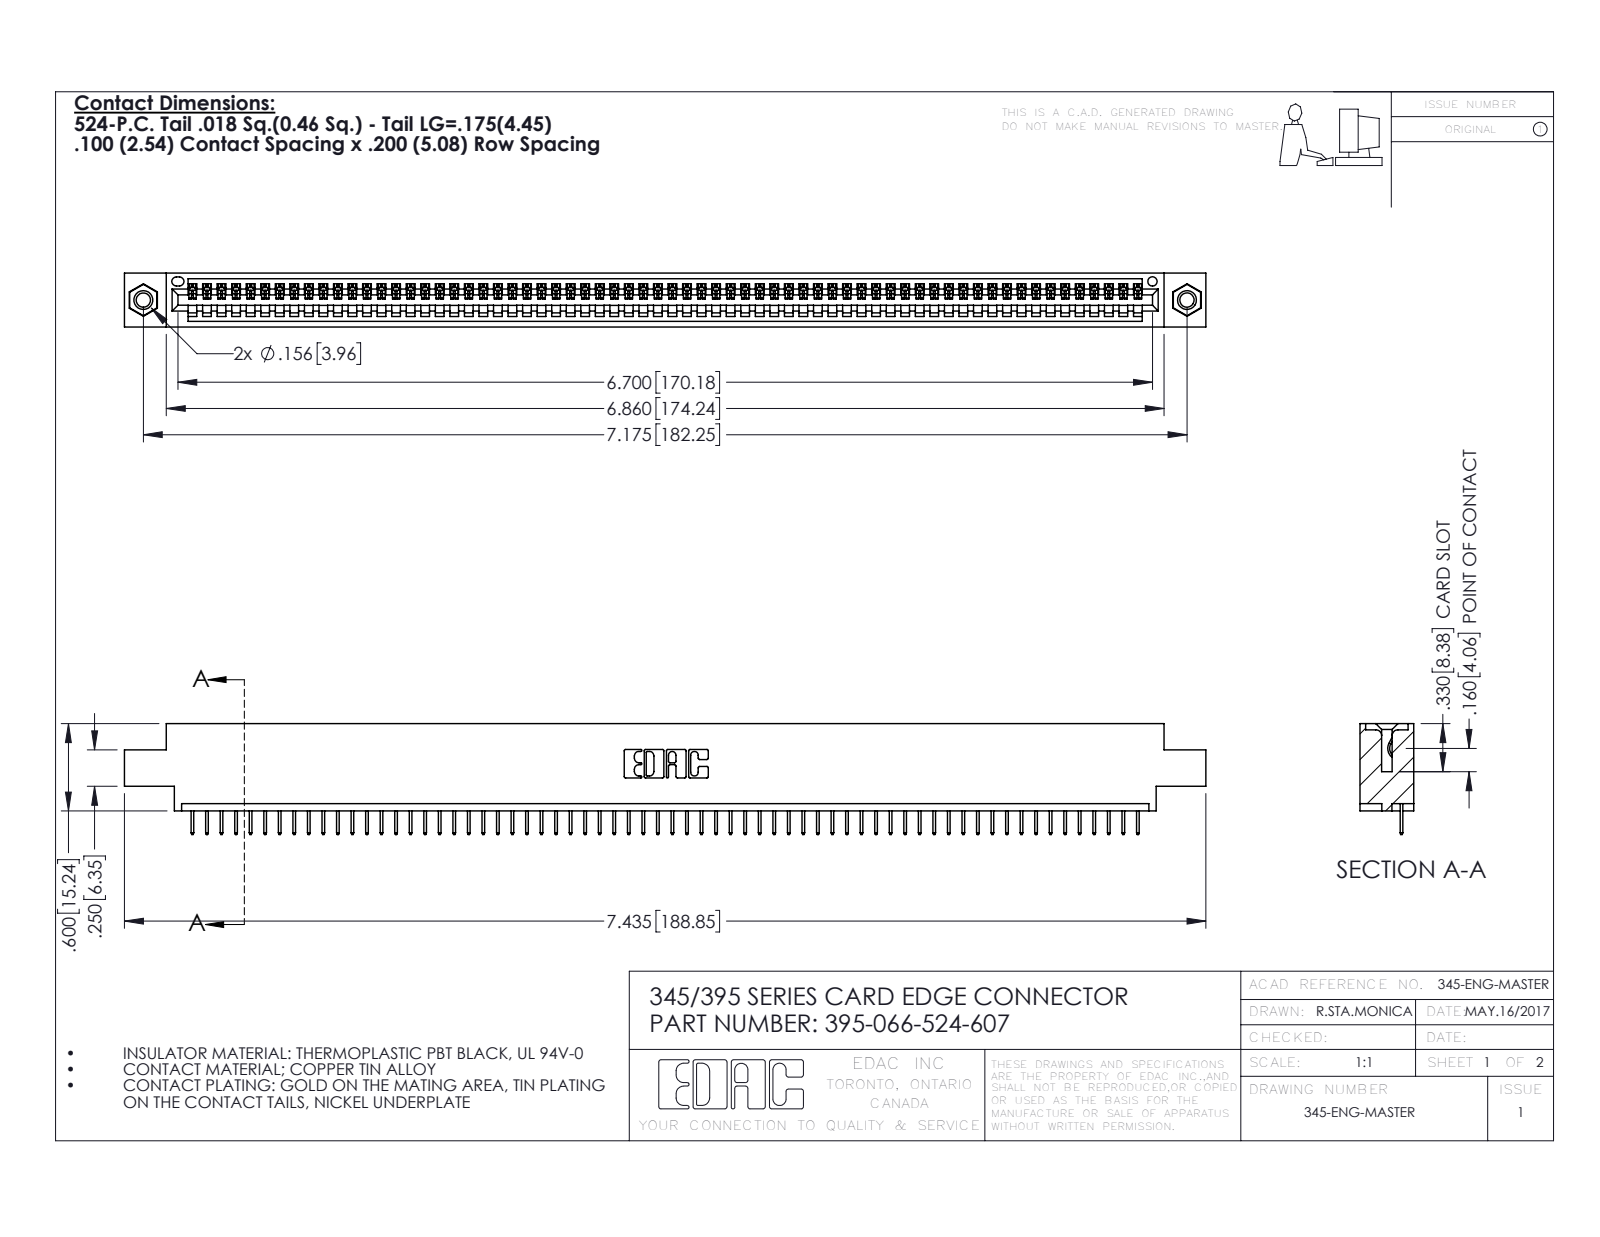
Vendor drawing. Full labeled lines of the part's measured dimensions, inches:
Part name (STEP PRODUCT): 345-292-001_345-293-124; 345-250-001_345-250-005-103; 345 Part_0.170 Offset - 0.156 Dia-TI; 395-066-524-607
STEP written by: SolidWorks 2016 (CONFIG_CONTROL_DESIGN)
Units: inches
Bodies: 69 solids, 4282 faces (3152 planar, 1114 cylindrical, 16 other)
Overall size (bounding box): 7.435 × 0.762 × 0.37
Volume: 1.083 in³ · Surface area: 36.01 in²
Round holes (diameter × count): ⌀0.098 ×2, ⌀0.125 ×2, ⌀0.156 ×2, ⌀0.064 ×1
Round bosses / shafts (diameter × count): ⌀0.155 ×2
Partial cylindrical surfaces — rounded edges, fillets, slot ends (radius × count): R0.006 ×132, R0.01 ×22, R0.007 ×6, R0.031 ×6, R0.026 ×3, R0.031 ×2, R0.04 ×2, R0.014 ×1
Main face-to-face distances: 0.072, 0.298, 0.37, 0.2, 0.098, 0.272, 0.025, 0.225, 0.072, 0.175
Hole centre spacings: 0.27, 6.939, 7.175
